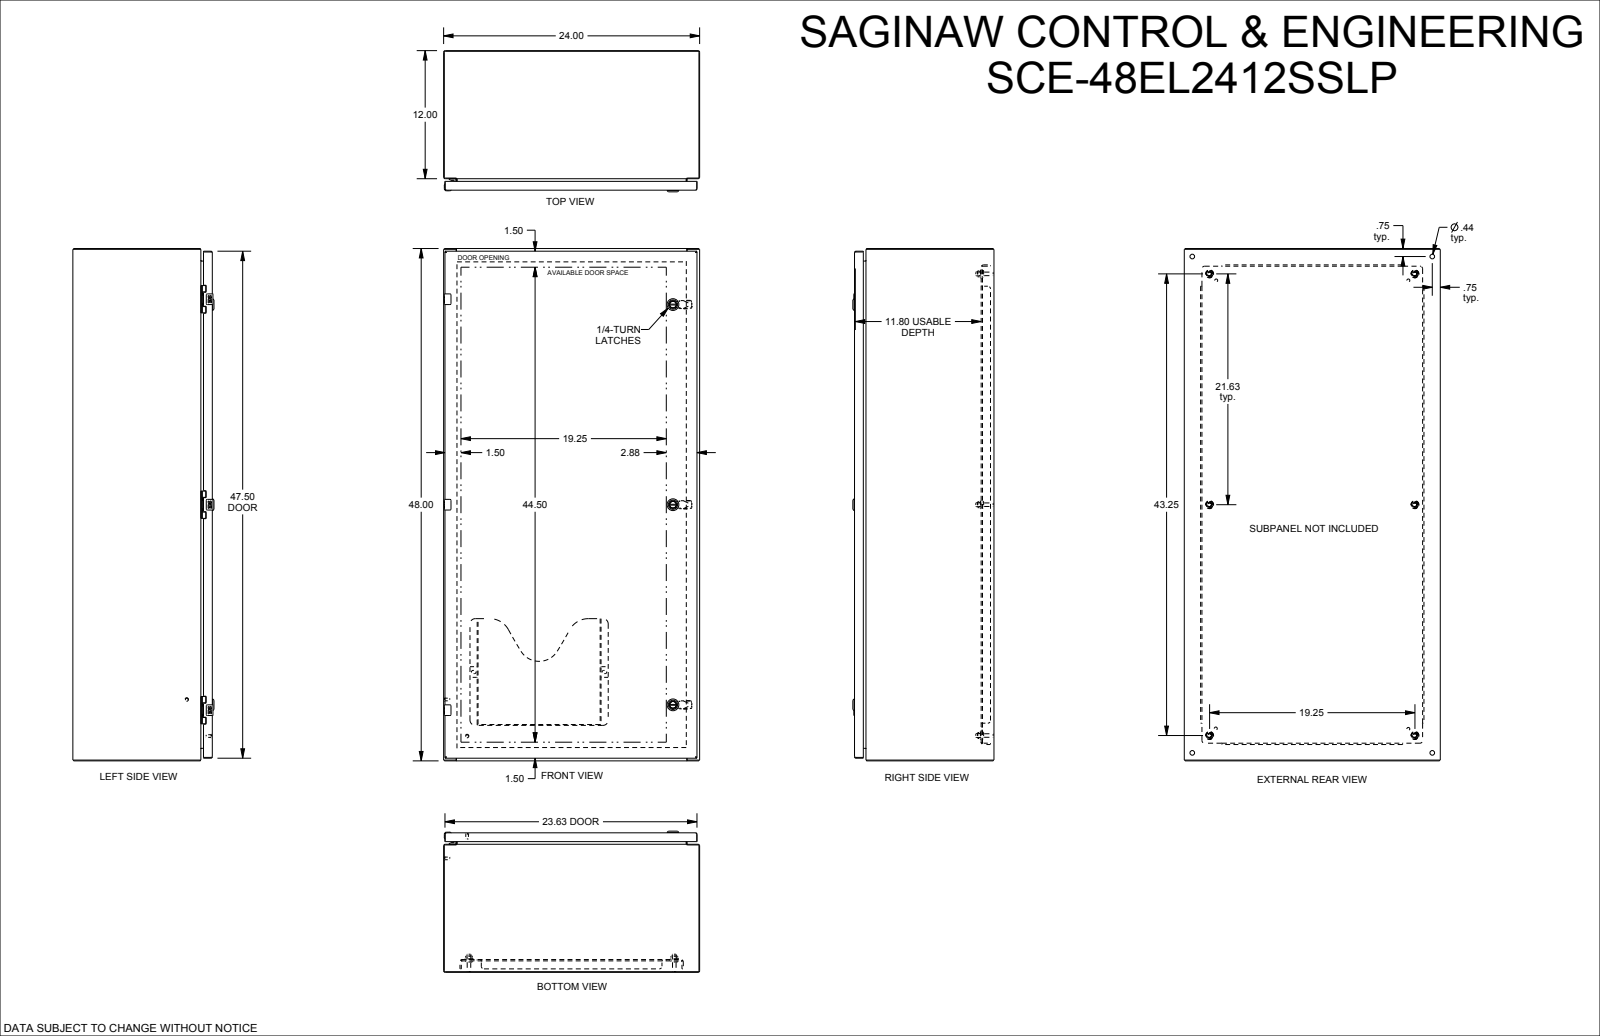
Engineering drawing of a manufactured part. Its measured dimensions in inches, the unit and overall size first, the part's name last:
Units: inches
Overall size (bounding box): 48 × 24 × 13.23
Round holes (diameter × count): ⌀0.394 ×13, ⌀0.172 ×6, ⌀0.205 ×6, ⌀0.244 ×6, ⌀0.266 ×6, ⌀0.367 ×6, ⌀0.5 ×6, ⌀0.281 ×4, ⌀0.375 ×4, ⌀0.437 ×4, ⌀0.156 ×3, ⌀0.197 ×3
Round bosses / shafts (diameter × count): ⌀0.17 ×9, ⌀0.366 ×6, ⌀0.332 ×6, ⌀0.25 ×6, ⌀0.248 ×4, ⌀0.196 ×4, ⌀1.102 ×3, ⌀0.866 ×3
Partial cylindrical surfaces — rounded edges, fillets, slot ends (radius × count): R0.012 ×82, R0.01 ×40, R0.015 ×36, R0.02 ×28, R0.04 ×23, R0.03 ×13, R0.029 ×12, R0.031 ×12
Main face-to-face distances: 0.075, 0.075, 1, 12.923, 12.998, 23.925, 13.073, 12.998, 1.2, 11.873
Hole centre spacings: 2.461, 19.25, 1.274, 3.48, 4.262, 4.754, 38.5, 0.985
Bodies: 0 solids, 4035 faces (1914 planar, 1128 cylindrical, 993 other)
Part name (STEP PRODUCT): SCE-48EL2412SSLP
STEP written by: SolidWorks 2019 (CONFIG_CONTROL_DESIGN)
